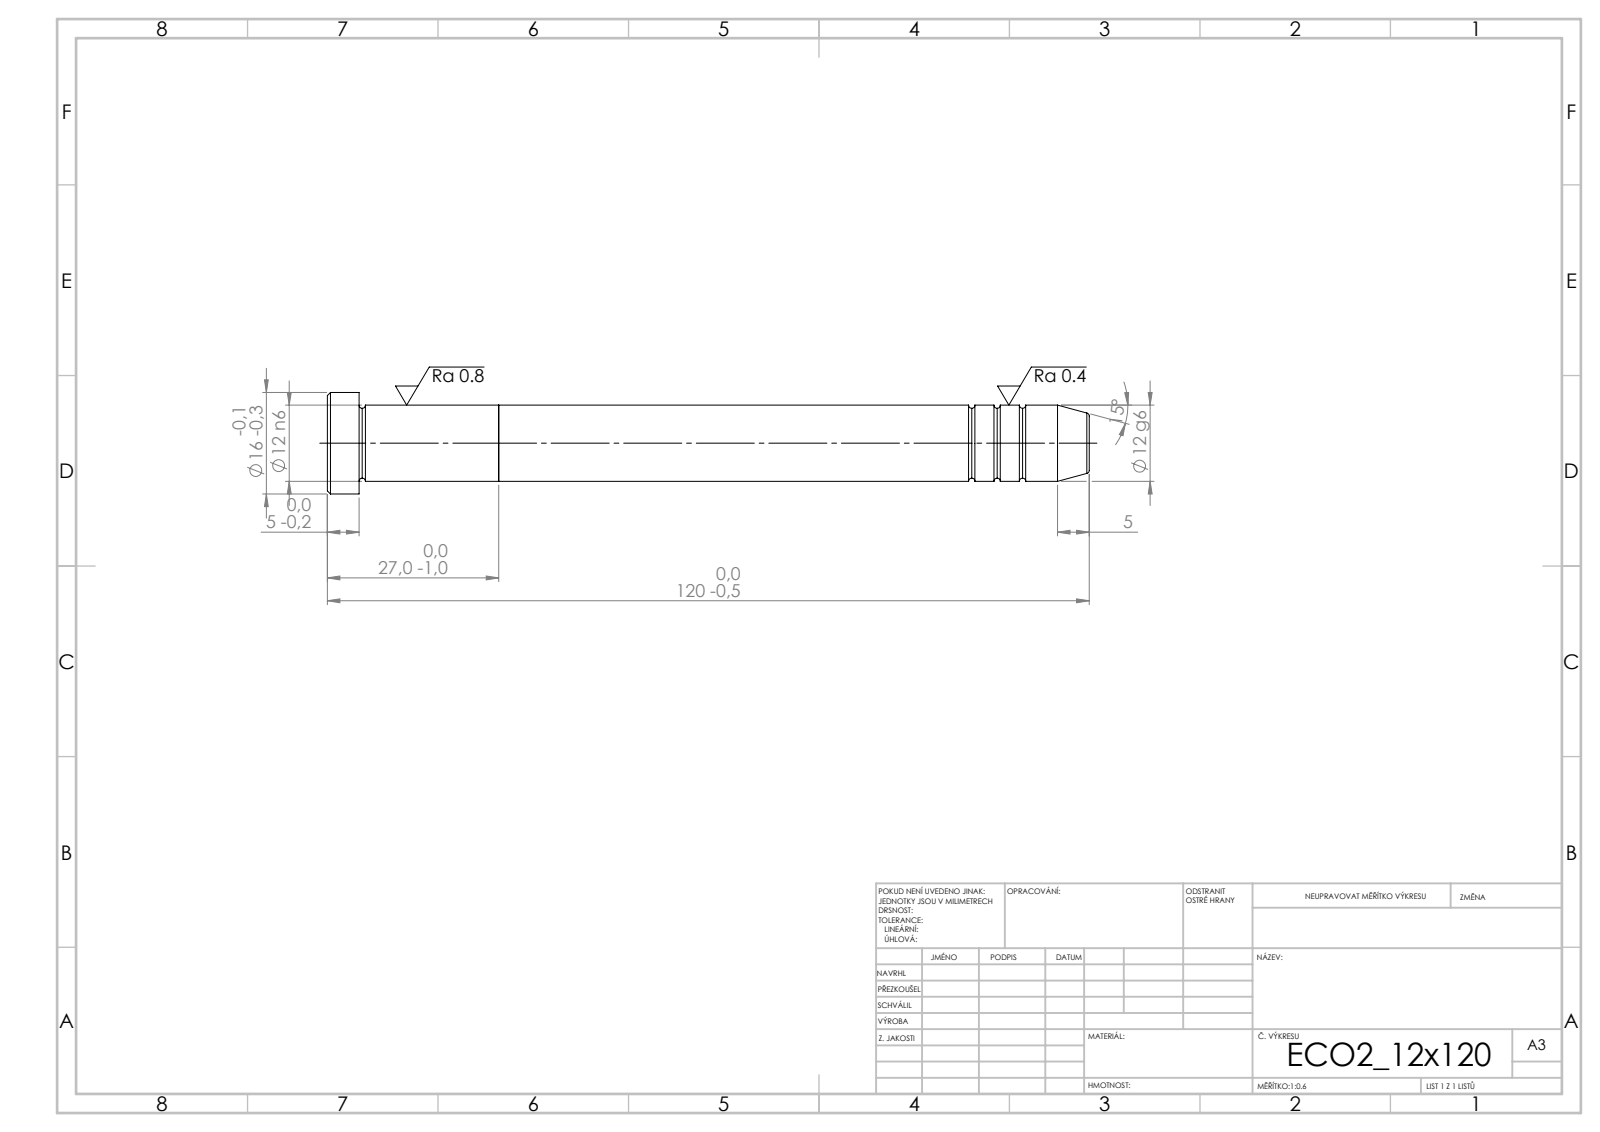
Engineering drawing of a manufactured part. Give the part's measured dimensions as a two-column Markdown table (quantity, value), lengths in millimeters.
| quantity | value |
| --- | --- |
| STEP written by | SolidWorks 2019 (CONFIG_CONTROL_DESIGN) |
| units | millimeters |
| bodies | 2 solids, 39 faces (5 planar, 12 cylindrical, 22 other) |
| overall size | 120 × 16 × 16 |
| volume | 13 831 mm³ |
| surface area | 5 210 mm² |
| round bosses / shafts (diameter × count) | 16 × 1, 12 × 1 |
| main face-to-face distances | 27, 22, 5, 93, 115, 120 |
